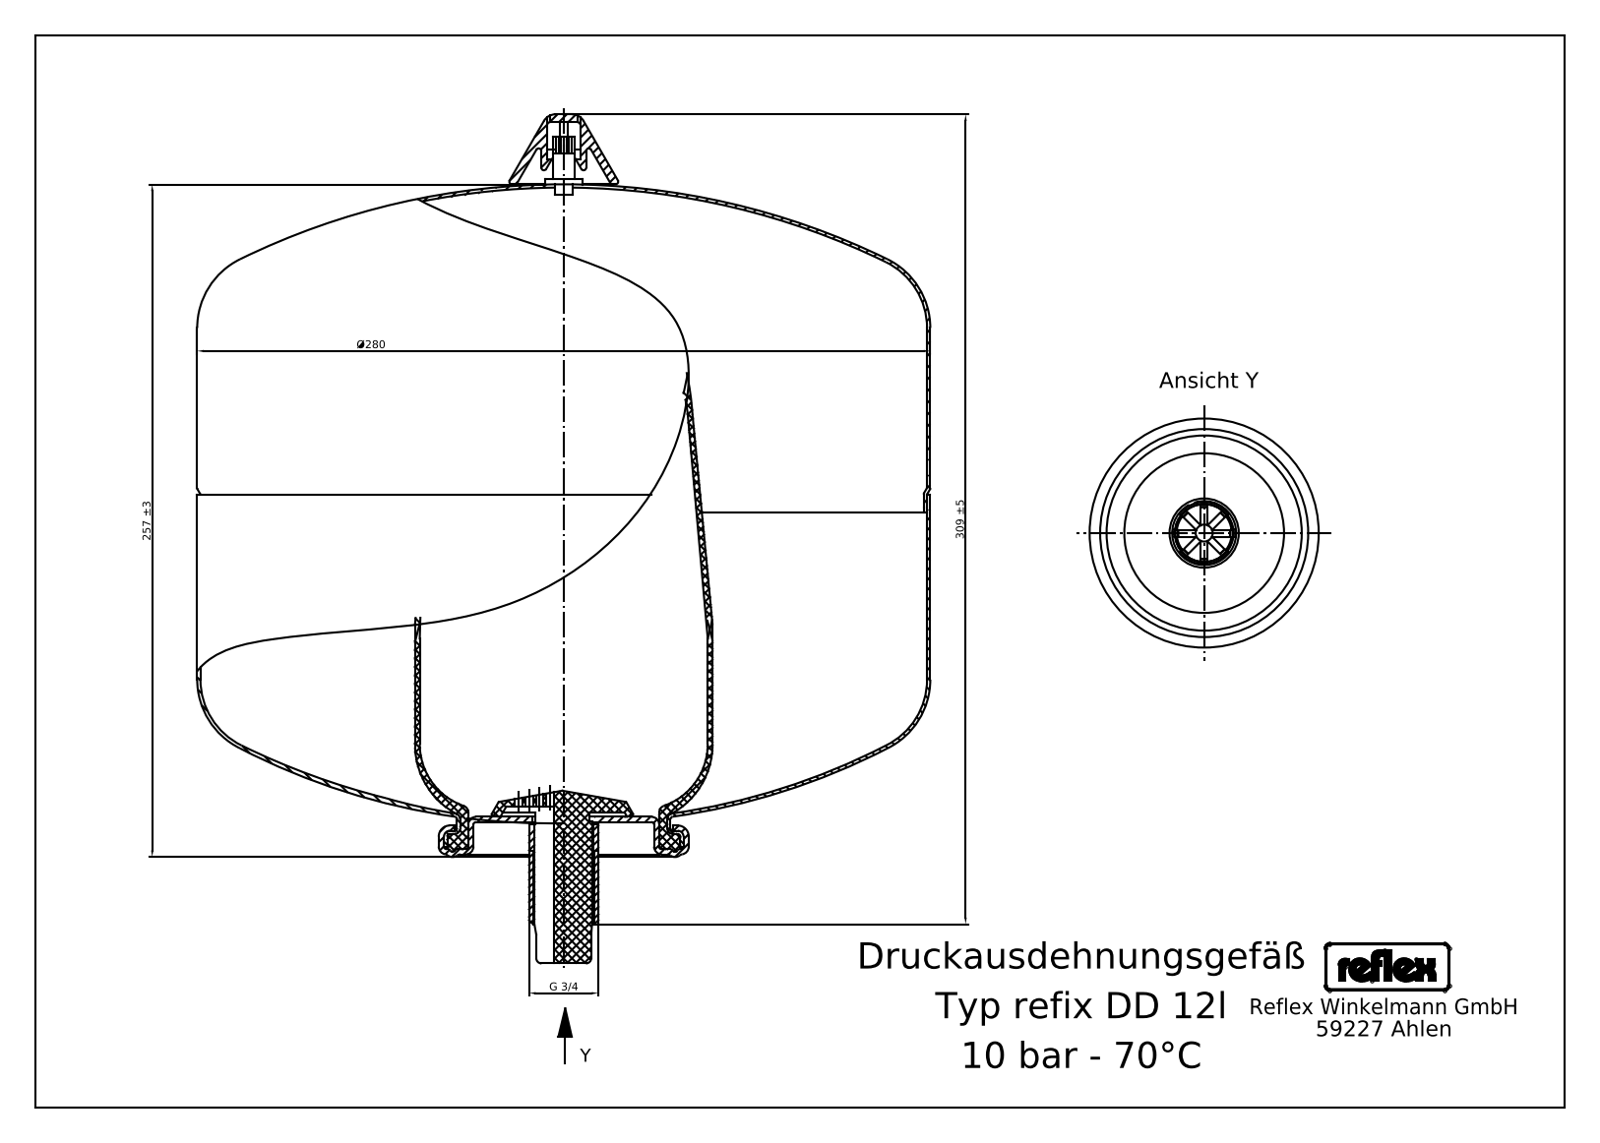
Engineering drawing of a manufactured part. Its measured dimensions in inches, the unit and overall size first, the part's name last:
Units: inches
Overall size (bounding box): 12.795 × 11.036 × 11.024
Round holes (diameter × count): ⌀0.555 ×1, ⌀0.744 ×1
Round bosses / shafts (diameter × count): ⌀11.024 ×1, ⌀3.78 ×1, ⌀3.228 ×1, ⌀1.059 ×1, ⌀0.673 ×1, ⌀0.354 ×1, ⌀0.236 ×1
Partial cylindrical surfaces — rounded edges, fillets, slot ends (radius × count): R0.044 ×4, R0.018 ×3, R0.03 ×2, R0.053 ×2, R0.073 ×2, R0.074 ×2, R0.1 ×2, R0.022 ×1
Main face-to-face distances: 5.354, 1.929, 7.283, 0.512, 2.441, 7.795, 0.059, 5.098, 4.587, 2.657
Volume: 787.8 in³ · Surface area: 885.2 in²
Bodies: 14 solids, 217 faces (129 planar, 46 cylindrical, 42 other)
STEP written by: Mechanical Desktop 2008 (CONFIG_CONTROL_DESIGN)
